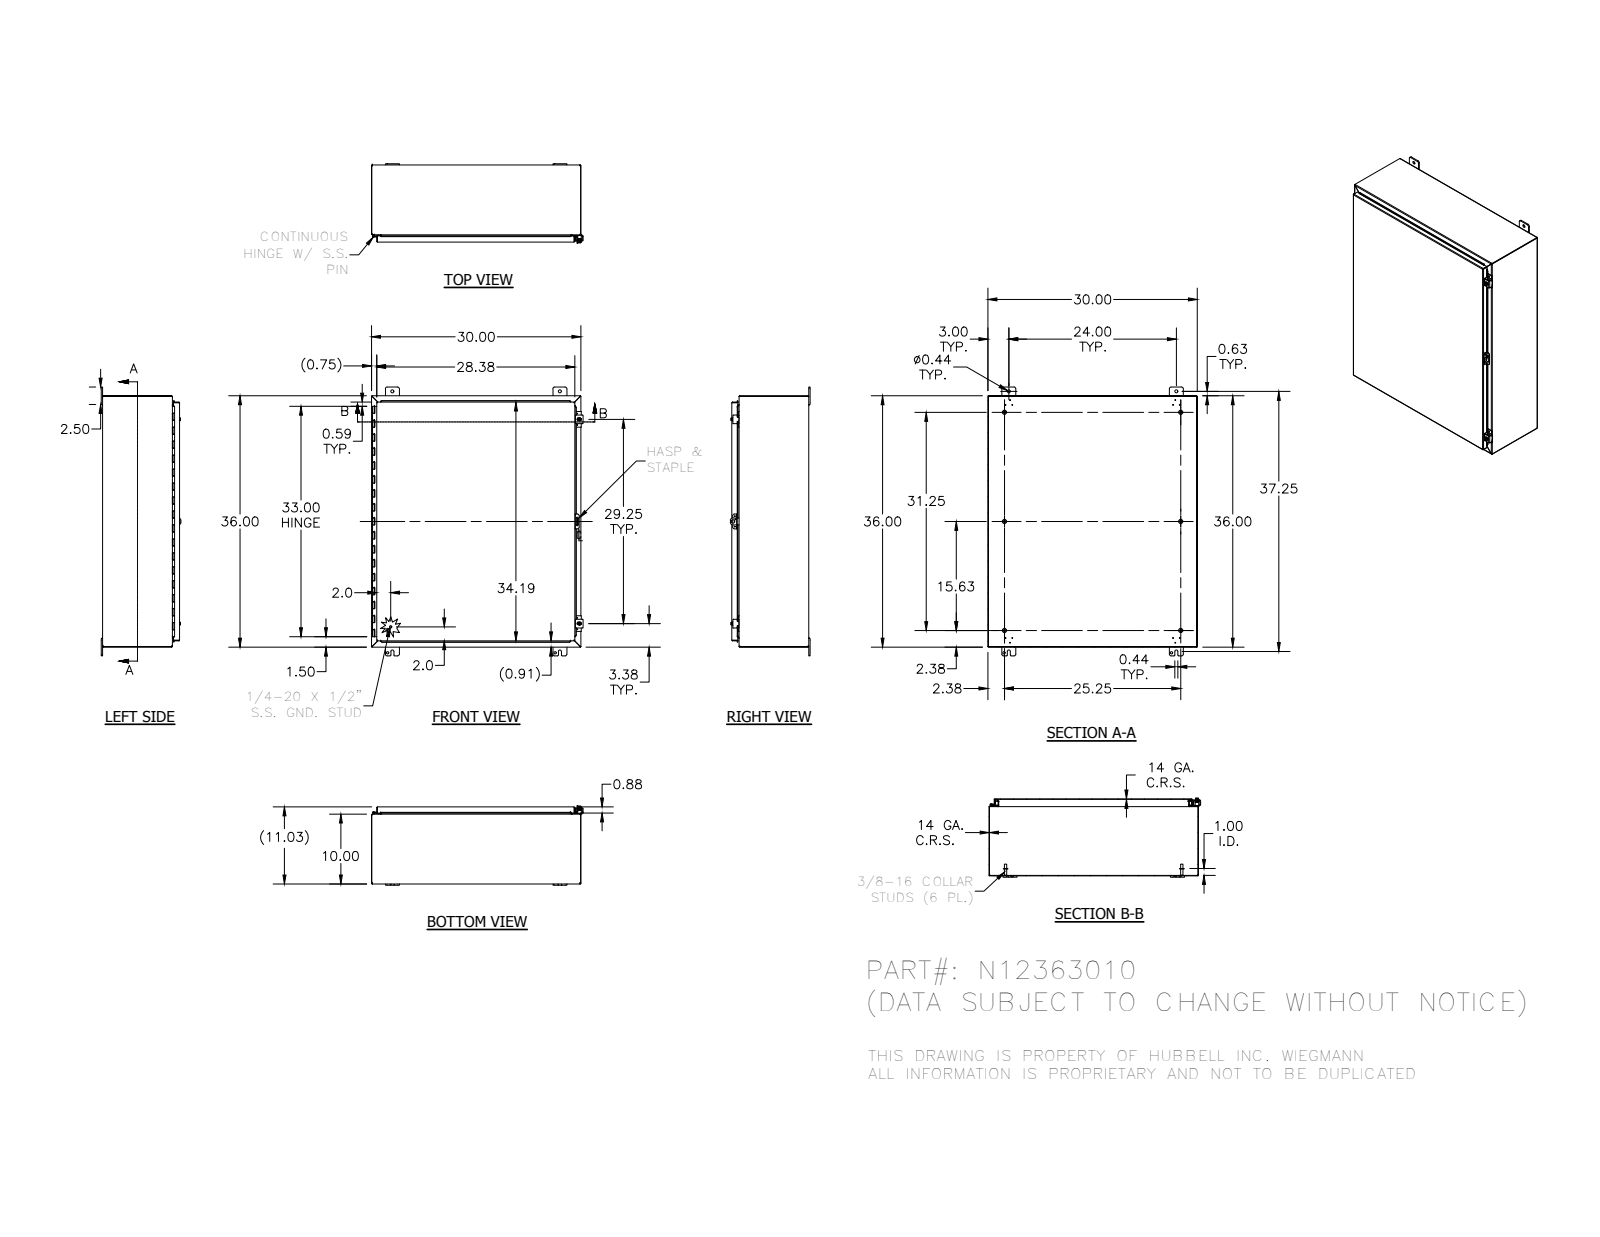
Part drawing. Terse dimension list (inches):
name: N12363010; 34840; 38420; N12363010BKP (+8 more)
written by: Autodesk Inventor 2012 (AUTOMOTIVE_DESIGN)
unit: in
bodies: 29 solids, 1100 faces (607 planar, 374 cylindrical, 119 other)
size: 38.5 × 30.311 × 11.41
volume: 300.6 in³; area: 7 924 in²
holes: 12× ⌀0.12, 7× ⌀0.11, 4× ⌀0.313, 4× ⌀0.438, 2× ⌀0.211, 2× ⌀0.281, 2× ⌀0.3, 1× ⌀0.125, 1× ⌀0.156, 1× ⌀0.5
bosses: 6× ⌀0.625, 6× ⌀0.33, 4× ⌀0.25, 2× ⌀0.52, 2× ⌀0.5, 2× ⌀0.35, 2× ⌀0.115, 1× ⌀0.337
rounds: 27× R0.03, 25× R0.063, 25× R0.125, 25× R0.25, 23× R0.031, 23× R0.105, 8× R0.07, 4× R0.1
face distances: 0.074, 10.959, 10.885, 11.033, 29.926, 35.926, 29.852, 30, 9.926, 1.033
hole spacings: 24, 0.759, 0.94, 0.969, 1.995, 23.367, 24.335, 33.38
